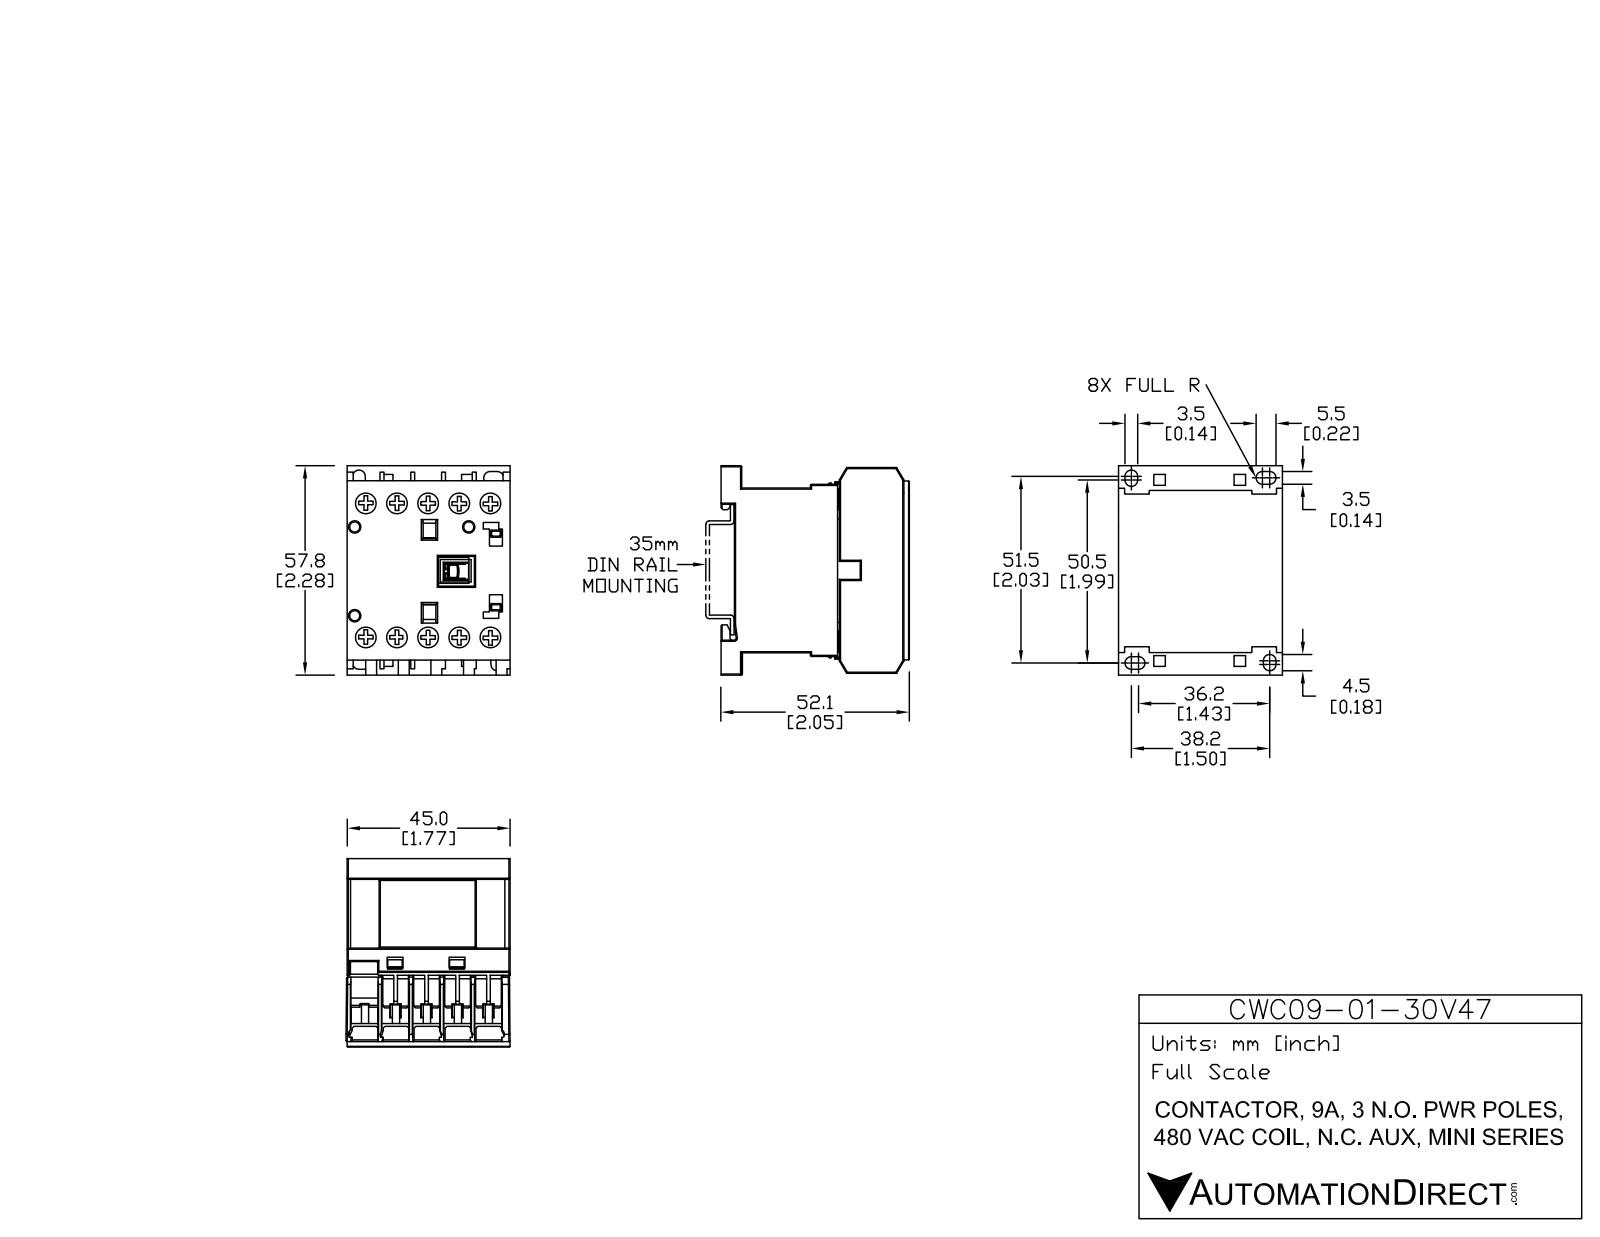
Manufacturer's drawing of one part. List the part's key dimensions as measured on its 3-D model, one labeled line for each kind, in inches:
Part name (STEP PRODUCT): CWC09-01-30V47
STEP written by: SolidWorks 2013 (AUTOMOTIVE_DESIGN)
Units: inches
Bodies: 15 solids, 535 faces (445 planar, 90 cylindrical, 0 other)
Overall size (bounding box): 2.285 × 2.052 × 1.801
Volume: 5.927 in³ · Surface area: 47.18 in²
Round holes (diameter × count): ⌀0.244 ×10, ⌀0.11 ×3
Round bosses / shafts (diameter × count): ⌀0.232 ×10
Partial cylindrical surfaces — rounded edges, fillets, slot ends (radius × count): R0.012 ×20, R0.068 ×6, R0.068 ×2, R0.013 ×1, R0.017 ×1, R0.022 ×1
Main face-to-face distances: 0.325, 1.791, 0.049, 0.65, 0.374, 0.217, 0.699, 0.202, 0.419, 0.276
Hole centre spacings: 0.337, 1.494, 0.673, 1.603, 1.455, 1.01, 1.771, 0.272
